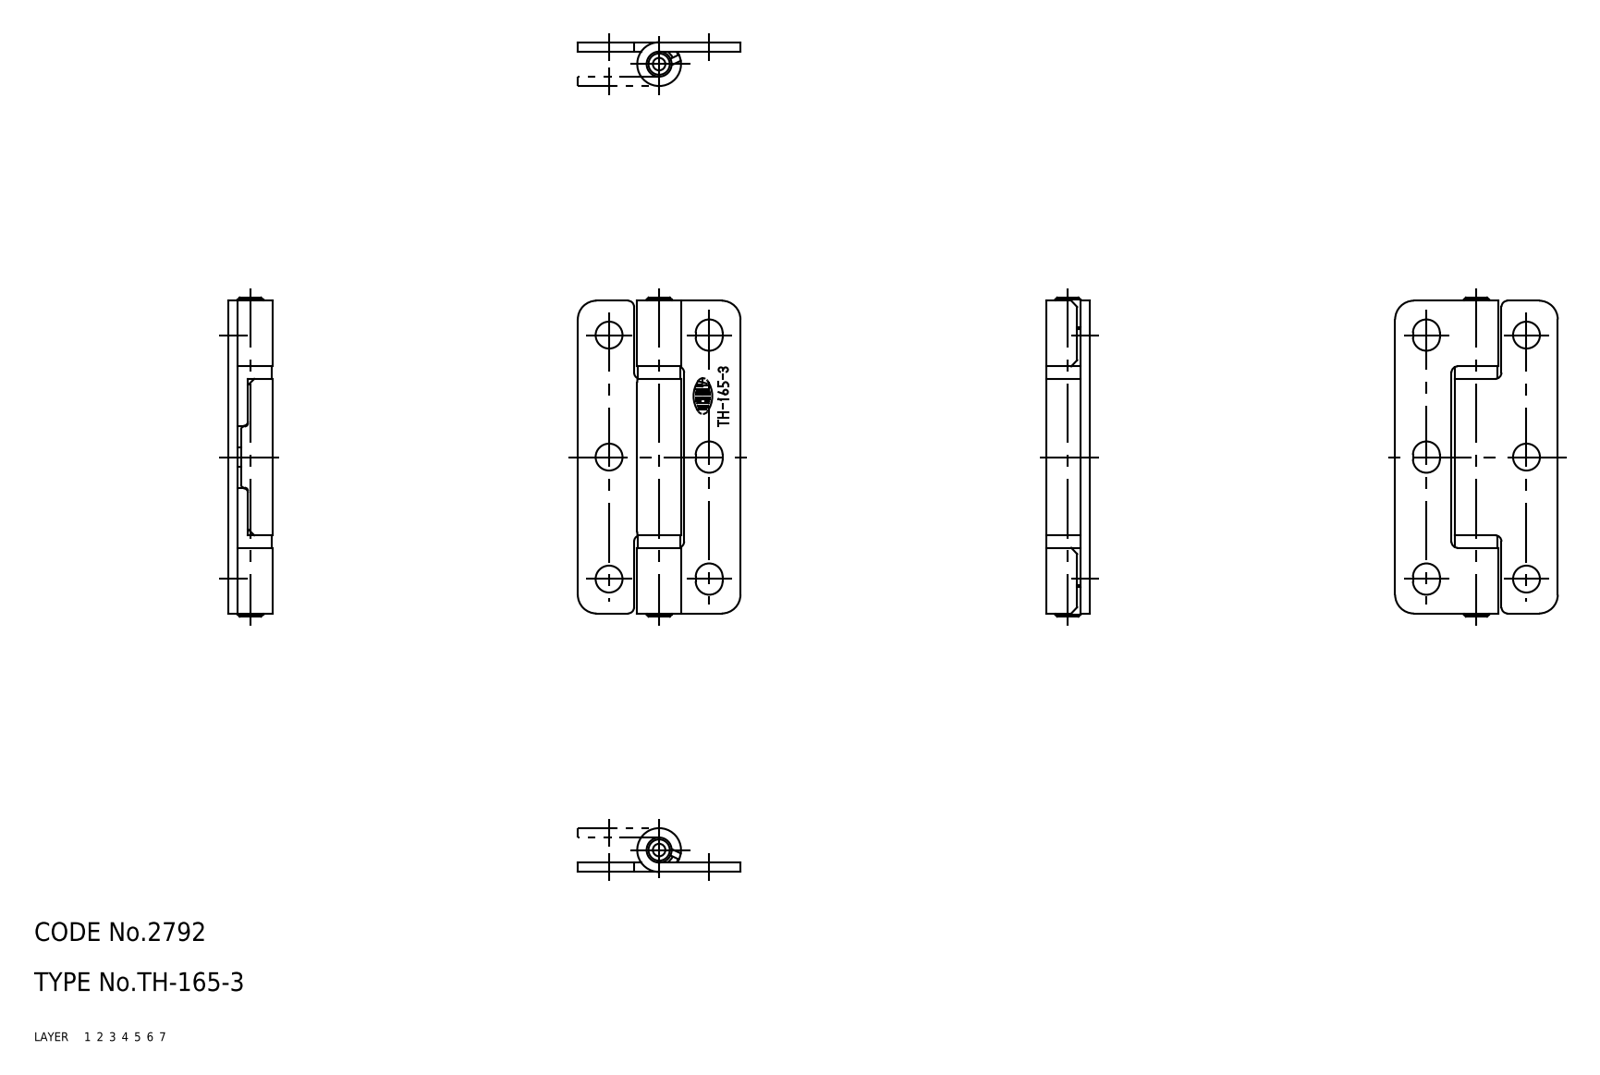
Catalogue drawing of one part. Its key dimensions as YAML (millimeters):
part_name: "67116352; 67116365; 67116378; 67116391 (+2 more)"
step_written_by: "CADfix (AUTOMOTIVE_DESIGN)"
units: millimeters
bodies: {solids: 6, faces: 124, planar: 0, cylindrical: 0, other: 124}
overall_size: [51, 26, 7]
volume: 3025
surface_area: 5072
